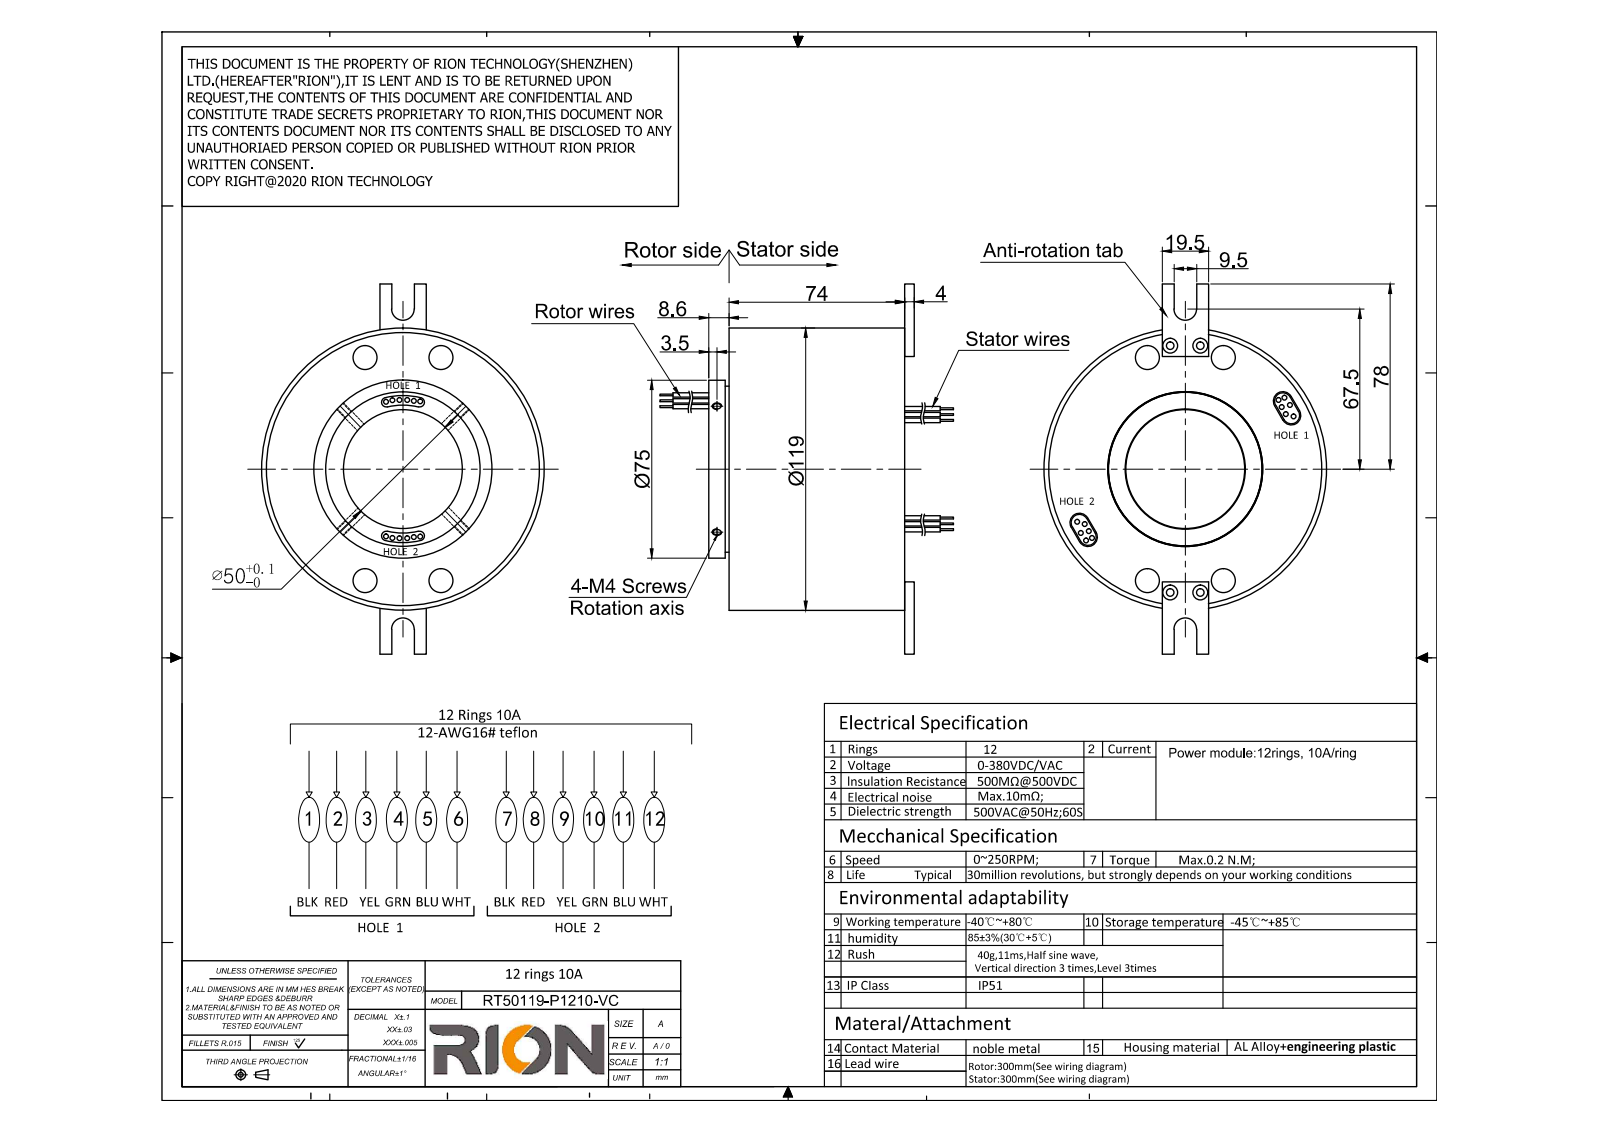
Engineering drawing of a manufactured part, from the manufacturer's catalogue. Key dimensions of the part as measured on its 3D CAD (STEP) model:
Part name (STEP PRODUCT): MT50119-P1210
STEP written by: SolidWorks 2014 (CONFIG_CONTROL_DESIGN)
Units: millimetres
Bodies: 1 solid, 193 faces (67 planar, 110 cylindrical, 16 other)
Overall size (bounding box): 156 × 120.6 × 119
Volume: 701 934 mm³ · Surface area: 73 928 mm²
Round holes (diameter × count): ⌀2.5 ×4, ⌀3.2 ×4, ⌀3.3 ×4, ⌀50 ×1, ⌀54 ×1, ⌀115 ×1
Round bosses / shafts (diameter × count): ⌀2.1 ×24, ⌀119 ×1, ⌀114.8 ×1, ⌀75 ×1, ⌀70 ×1, ⌀53.8 ×1
Partial cylindrical surfaces — rounded edges, fillets, slot ends (radius × count): R2 ×4, R2.5 ×4, R4.75 ×2, R31 ×1
Main face-to-face distances: 74, 8.6, 82.6, 86.6, 78, 4, 79.6, 7, 1.6, 75.6
Hole centre spacings: 52.39, 12.7, 104, 104.77
